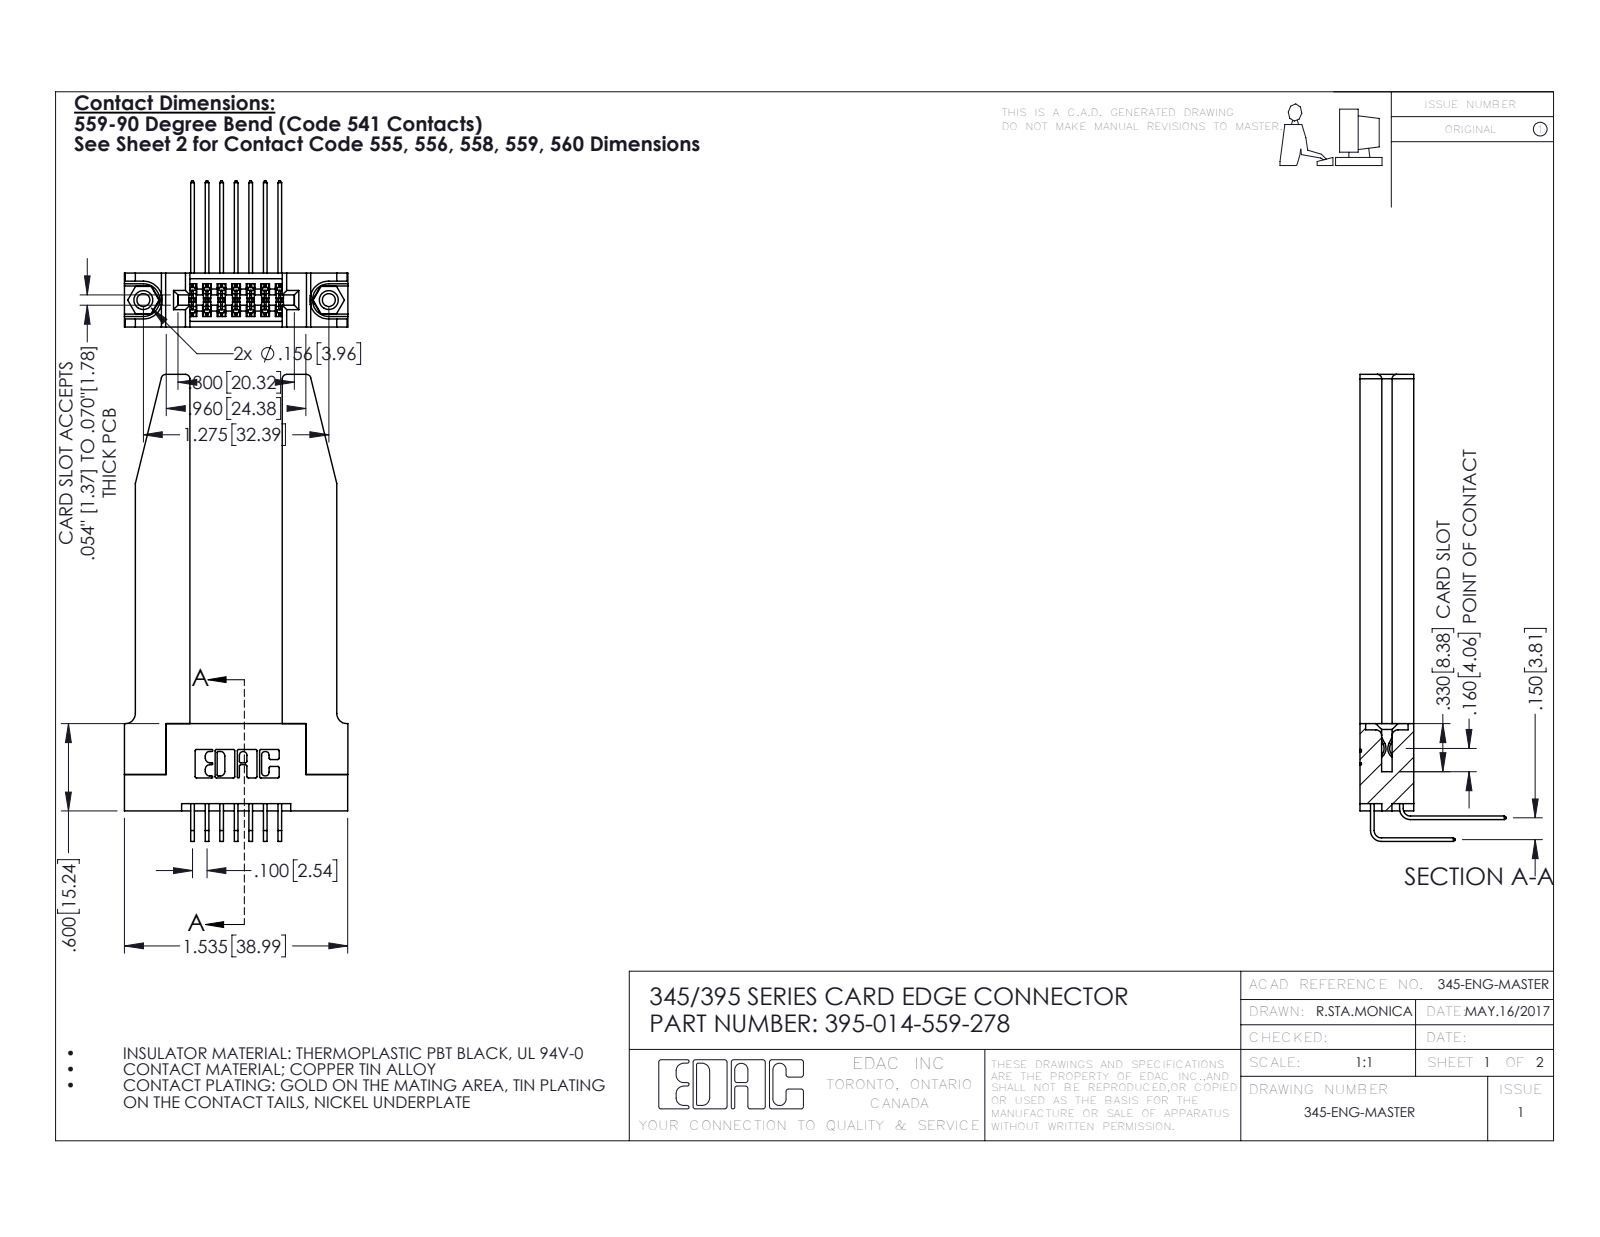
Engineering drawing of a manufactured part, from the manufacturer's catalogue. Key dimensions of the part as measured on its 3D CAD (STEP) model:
Part name (STEP PRODUCT): 345-292-001_559 Tail - 2; 395-014-559-278; 345-220-078_345-220-078; 345-250-001_345-250-001-102 (+2 more)
STEP written by: SolidWorks 2016 (CONFIG_CONTROL_DESIGN)
Units: inches
Bodies: 19 solids, 1088 faces (712 planar, 324 cylindrical, 52 other)
Overall size (bounding box): 3.209 × 1.536 × 1.005
Volume: 0.691 in³ · Surface area: 18.26 in²
Round holes (diameter × count): ⌀0.089 ×2, ⌀0.125 ×2, ⌀0.156 ×2, ⌀0.064 ×1
Round bosses / shafts (diameter × count): ⌀0.155 ×2
Partial cylindrical surfaces — rounded edges, fillets, slot ends (radius × count): R0.006 ×22, R0.01 ×22, R0.03 ×8, R0.007 ×6, R0.031 ×6, R0.026 ×3, R0.014 ×2, R0.019 ×2
Main face-to-face distances: 0.37, 0.15, 0.072, 0.148, 0.22, 0.298, 0.077, 0.635, 0.2, 0.095
Hole centre spacings: 0.27, 1.045, 1.275
